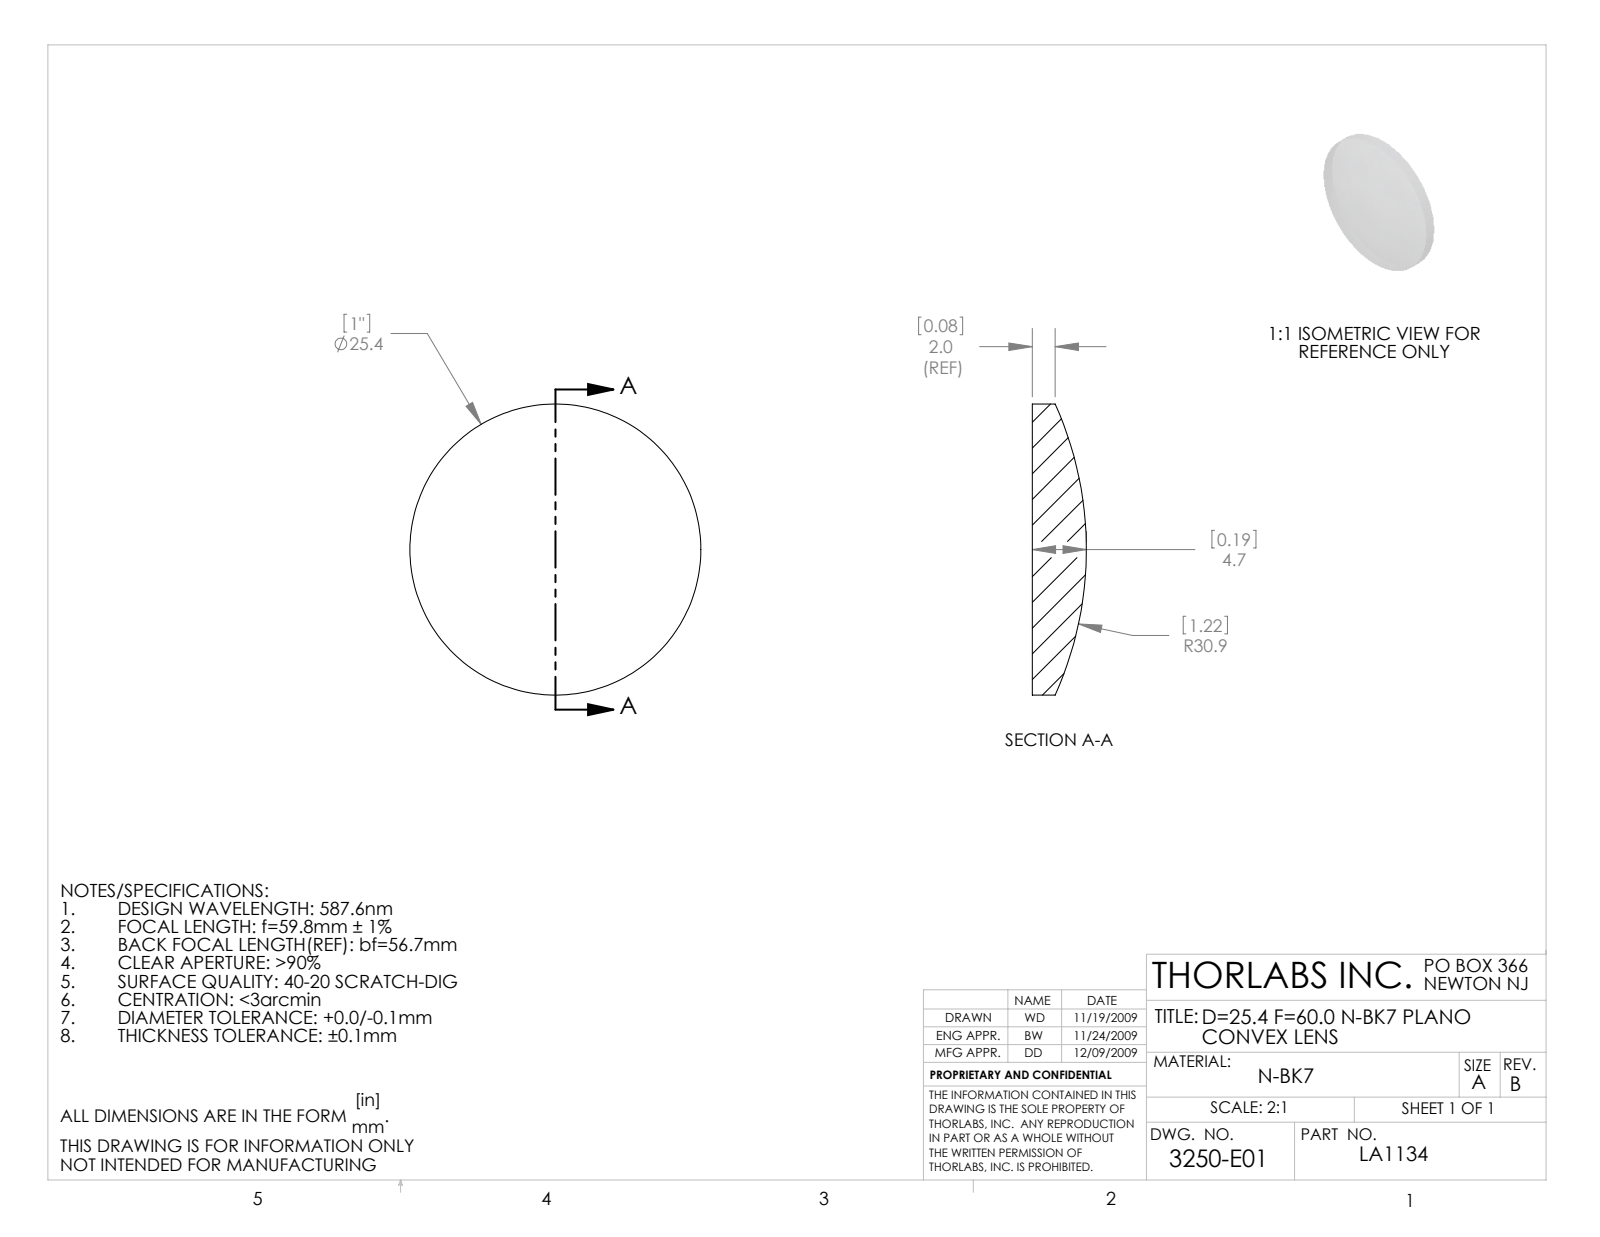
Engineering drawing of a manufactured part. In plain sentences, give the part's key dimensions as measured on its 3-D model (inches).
The part is named "3250-E0W". Its 3-D file was written by "SolidWorks 2016 (AUTOMOTIVE_DESIGN)". It is 1 solid with 5 faces: 1 planar, 2 cylindrical and 2 other. Overall it measures 1 by 1 by 0.186 inches. Its volume is 0.105 cubic inches and its surface area 1.854 square inches. Round bosses or shafts: 1 of diameter 1.
